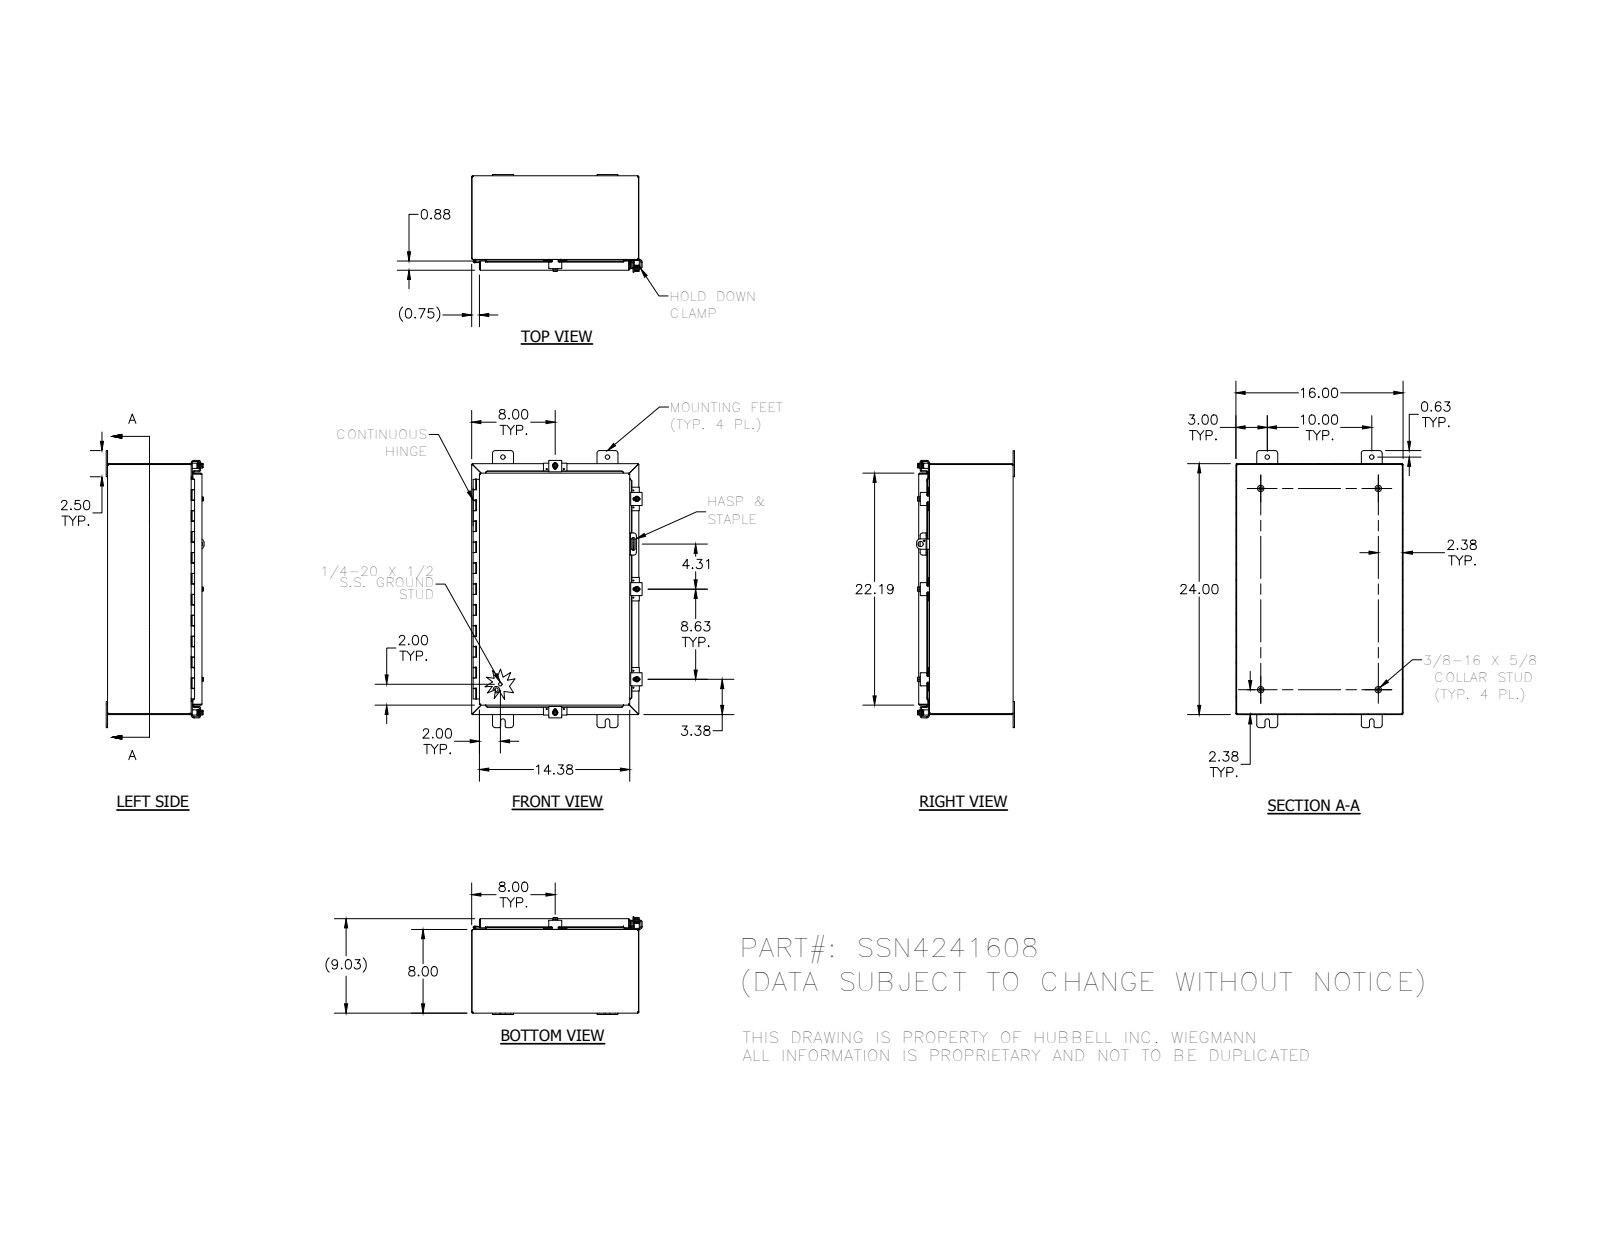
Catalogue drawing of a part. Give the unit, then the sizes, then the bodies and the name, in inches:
Units: inches
Overall size (bounding box): 26.5 × 16.311 × 9.355
Round holes (diameter × count): ⌀0.11 ×10, ⌀0.211 ×5, ⌀0.281 ×5, ⌀0.3 ×5, ⌀0.438 ×4, ⌀0.125 ×1, ⌀0.156 ×1, ⌀0.5 ×1
Round bosses / shafts (diameter × count): ⌀0.25 ×7, ⌀0.52 ×5, ⌀0.5 ×5, ⌀0.35 ×5, ⌀0.625 ×4, ⌀0.33 ×4, ⌀0.115 ×2, ⌀0.337 ×1
Partial cylindrical surfaces — rounded edges, fillets, slot ends (radius × count): R0.03 ×61, R0.125 ×35, R0.25 ×31, R0.031 ×23, R0.105 ×23, R0.062 ×13, R0.141 ×10, R0.07 ×8
Main face-to-face distances: 0.074, 8.959, 15.926, 8.885, 9.033, 23.926, 7.926, 1.033, 15.852, 16
Hole centre spacings: 0.876, 23.303, 1.625, 4.341, 7.82, 8.625, 8.625, 9.443
Volume: 132.1 in³ · Surface area: 3 458 in²
Bodies: 42 solids, 1674 faces (650 planar, 737 cylindrical, 287 other)
Part name (STEP PRODUCT): 30824_1; HFW30825-3_1; 328138T_1; 34871_1 (+8 more)
STEP written by: SolidWorks 2014 (AUTOMOTIVE_DESIGN)
